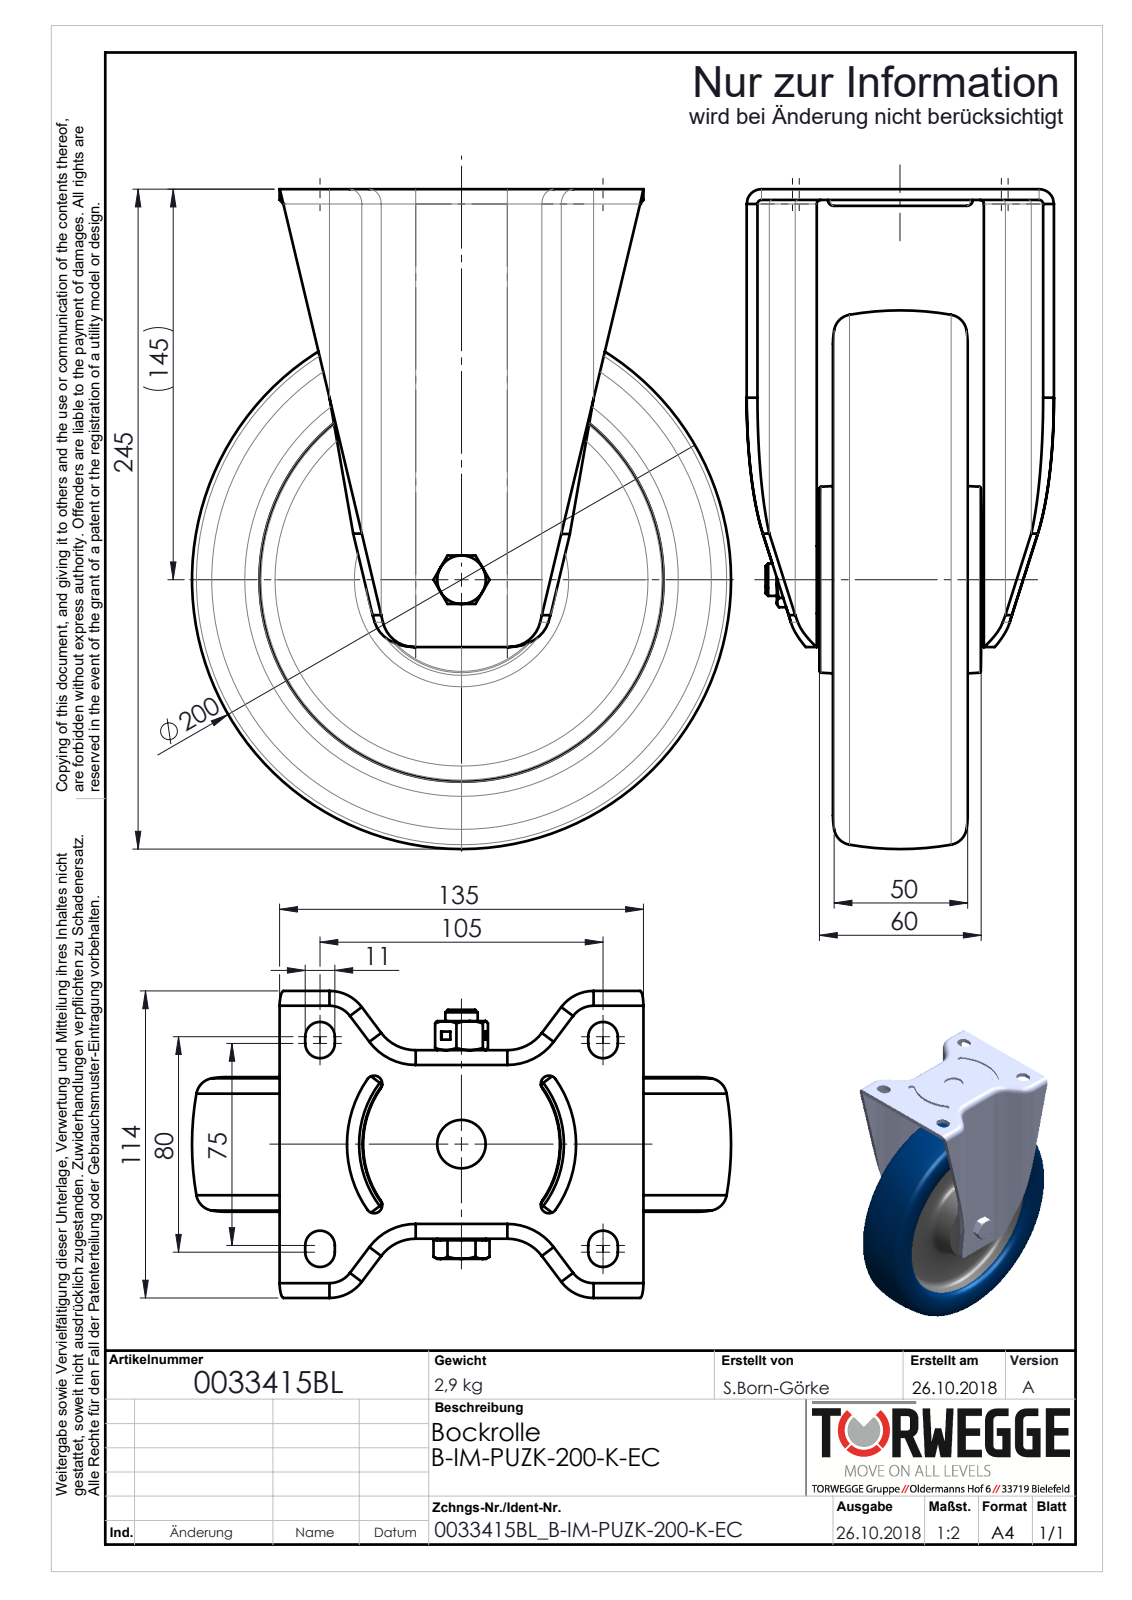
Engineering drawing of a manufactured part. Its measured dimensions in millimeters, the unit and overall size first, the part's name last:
Units: millimetres
Overall size (bounding box): 245 × 196.74 × 114
Round holes (diameter × count): ⌀10.2 ×1, ⌀12 ×1, ⌀12.2 ×1, ⌀12.5 ×1, ⌀18 ×1, ⌀20 ×1, ⌀20.5 ×1, ⌀38.9 ×1
Round bosses / shafts (diameter × count): ⌀28.1 ×1, ⌀25 ×1, ⌀19.9 ×1, ⌀18 ×1
Partial cylindrical surfaces — rounded edges, fillets, slot ends (radius × count): R5.5 ×16, R1.5 ×8, R2.2 ×4, R3 ×4, R11 ×4, R15 ×4, R16 ×4, R20 ×4
Main face-to-face distances: 4, 66, 2, 62, 70, 22, 88, 6, 18, 84
Bodies: 0 solids, 376 faces (108 planar, 100 cylindrical, 168 other)
Part name (STEP PRODUCT): 0033415BL_B-IM-PUZK-200-K-EC
STEP written by: SolidWorks 2018 (AUTOMOTIVE_DESIGN)
